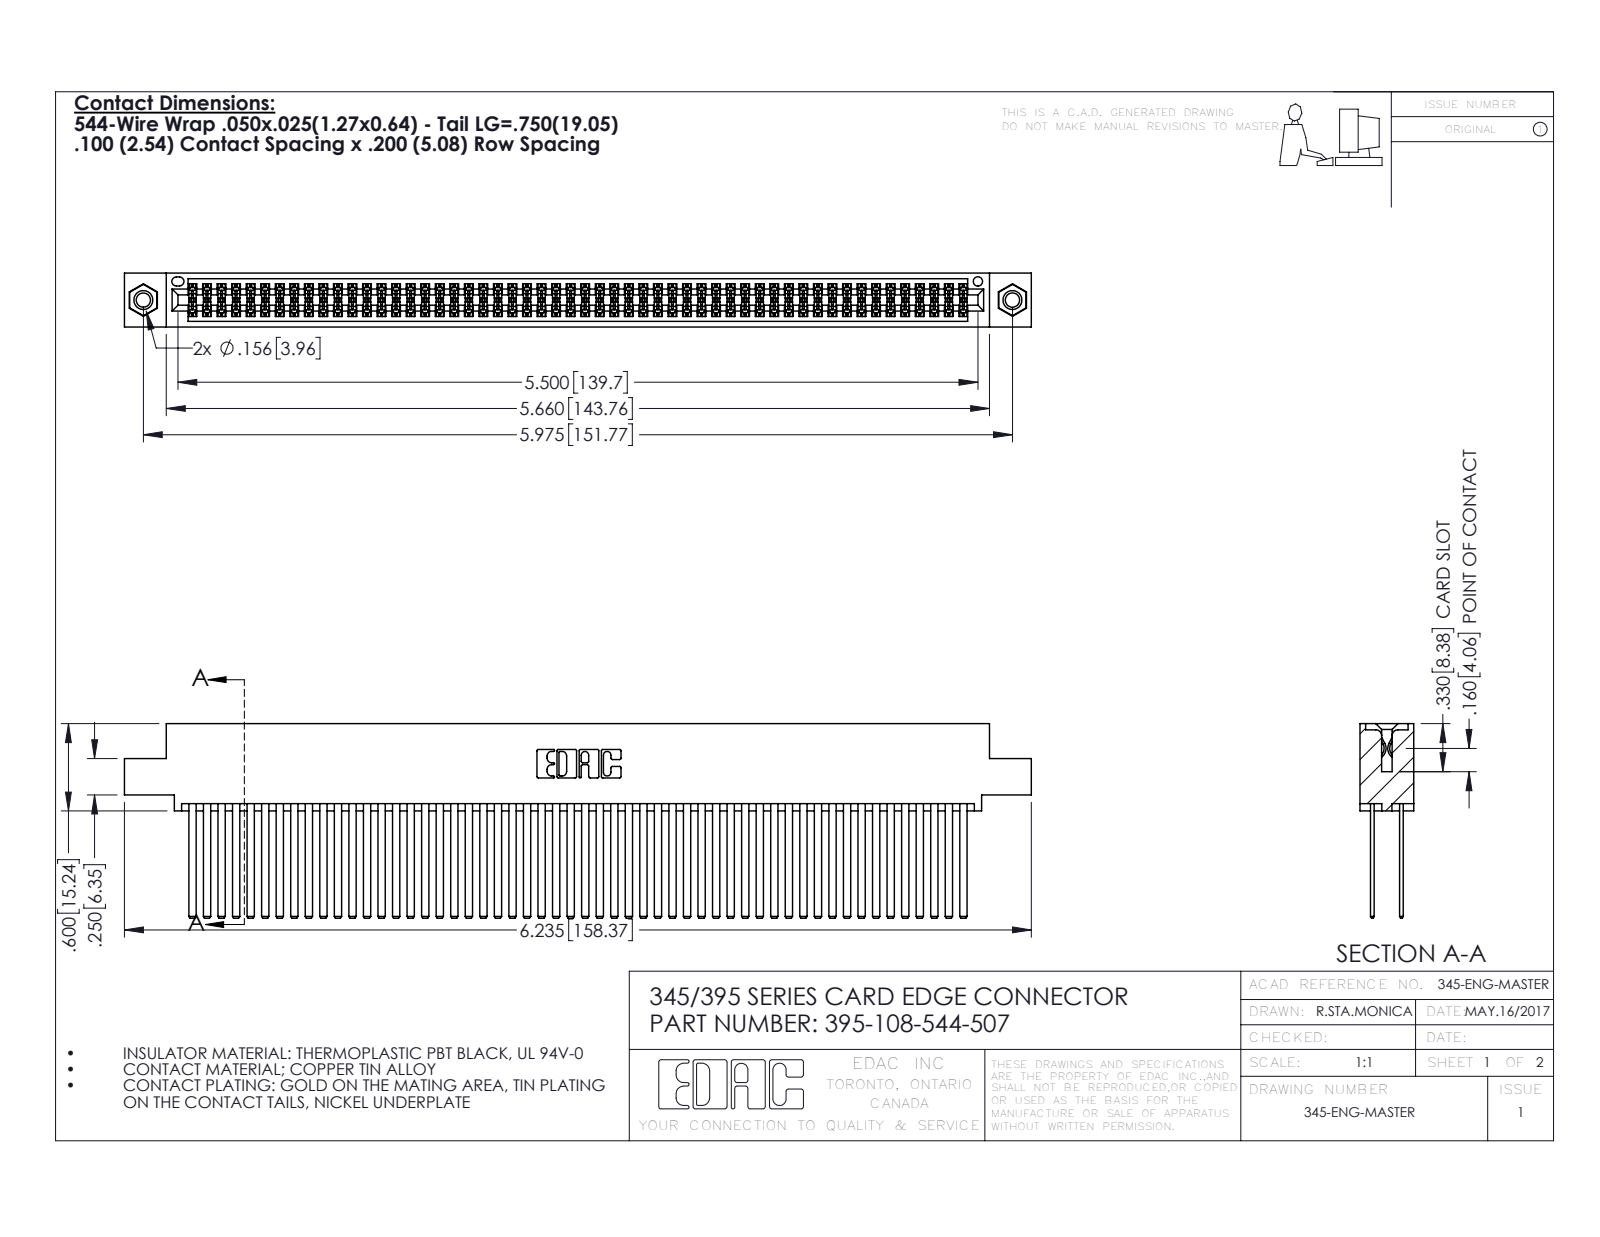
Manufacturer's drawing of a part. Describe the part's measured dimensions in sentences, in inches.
The part is named "345-250-001_345-250-005-103; 395-108-544-507; 345 Part_0.110 Offset - 0.156 Dia-TI; 345-292-001_345-293-144". Its 3-D file was written by "SolidWorks 2016 (CONFIG_CONTROL_DESIGN)". It is 111 solids with 4942 faces: 3248 planar, 1678 cylindrical and 16 other. Overall it measures 6.235 by 1.337 by 0.37 inches. Its volume is 1.033 cubic inches and its surface area 46.2 square inches. Round holes: 2 of diameter 0.098, 2 of diameter 0.125, 2 of diameter 0.156, 1 of diameter 0.064. Round bosses or shafts: 2 of diameter 0.155. Partial cylindrical surfaces (rounded edges, fillets, slot ends): 162 of radius 0.006, 22 of radius 0.01, 6 of radius 0.007, 6 of radius 0.031, 3 of radius 0.026, 2 of radius 0.014, 2 of radius 0.019, 2 of radius 0.022. The main face-to-face distances are 0.2, 0.025, 0.072, 0.098, 0.272, 0.298, 0.225, 0.175, 0.37, 0.05. The hole center spacings are 0.27, 5.739, 5.975.
